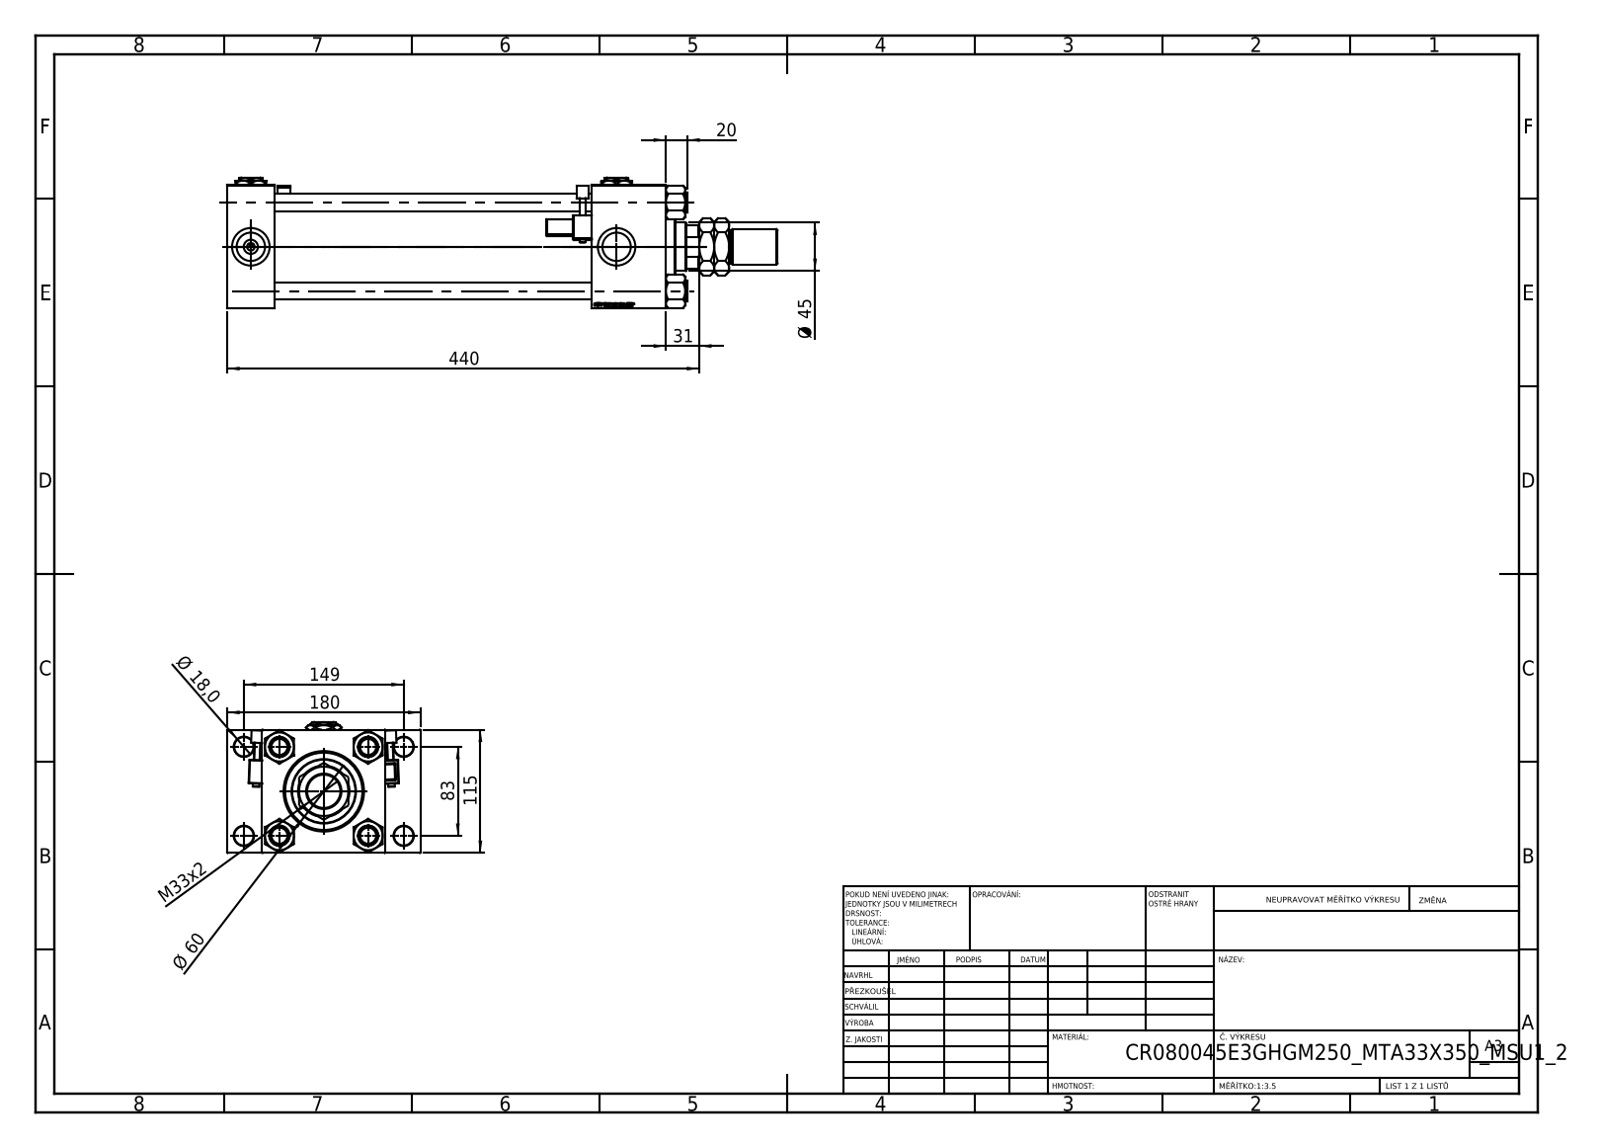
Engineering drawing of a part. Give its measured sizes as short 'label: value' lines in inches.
name: NUT_M5_E; V215_VC_A; V215CR_E_Body; V215CR_MSU (+4 more)
written by: SolidWorks 2019 (CONFIG_CONTROL_DESIGN)
unit: in
bodies: 16 solids, 1487 faces (666 planar, 161 cylindrical, 660 other)
size: 20.197 × 7.087 × 4.803
volume: 180.9 in³; area: 847.2 in²
holes: 4× ⌀0.63, 4× ⌀0.709, 4× ⌀1.041, 4× ⌀1.378, 3× ⌀0.276, 1× ⌀1.24, 1× ⌀1.772, 1× ⌀1.89, 1× ⌀2.402, 1× ⌀2.835, 1× ⌀3.15
bosses: 4× ⌀0.748, 2× ⌀0.236, 1× ⌀3.386, 1× ⌀2.362, 1× ⌀1.299, 1× ⌀1.22
rounds: 48× R0.02, 2× R0.039, 2× R0.098, 2× R0.157, 1× R0.866
face distances: 4.528, 1.732, 16.102, 14.37, 1.28, 13.386, 11.654, 2.717, 5.807, 1.811
hole spacings: 1.305, 2.302, 3.256, 3.357, 3.513, 4.561, 5.607, 3.268
